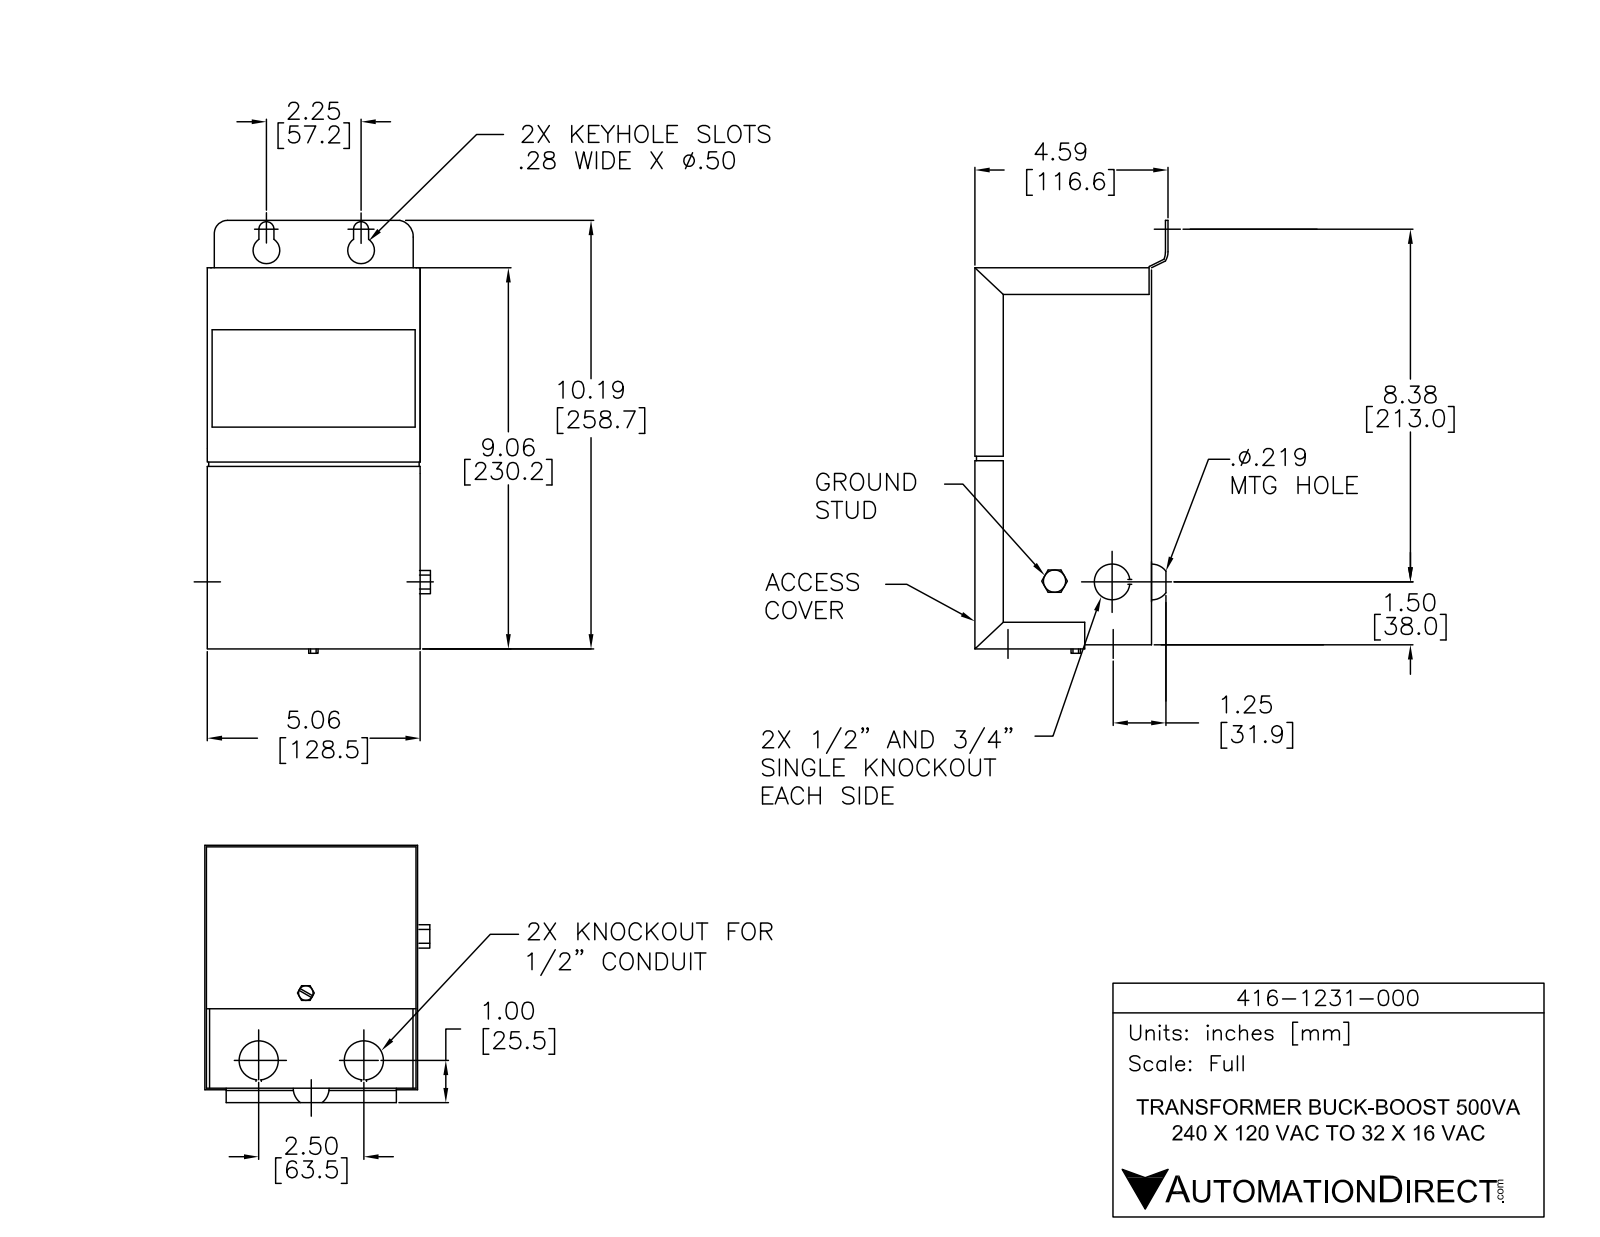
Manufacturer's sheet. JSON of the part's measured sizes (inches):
{"part_name": "416-1231-000", "step_written_by": "SolidWorks 2013 (AUTOMOTIVE_DESIGN)", "units": "inches", "bodies": {"solids": 1, "faces": 159, "planar": 91, "cylindrical": 52, "other": 16}, "overall_size": [10.3, 5.17, 4.591], "volume_in3": 190.3, "surface_area_in2": 225.3, "round_holes": [[0.5, 2], [0.875, 2], [0.219, 1], [0.232, 1], [0.29, 1], [0.875, 1]], "round_bosses_or_shafts": [[1.125, 1]], "partial_cylinders_radius": [[0.04, 10], [0.25, 10], [0.14, 2], [0.06, 1], [0.149, 1], [0.189, 1]], "face_to_face_distances": [4.2, 4.98, 0.04, 5.02, 4.201, 9.06, 5.06, 9.02, 0.04, 0.39], "hole_center_spacings": [1.719, 8.168, 1.37, 2.25, 2.5]}
